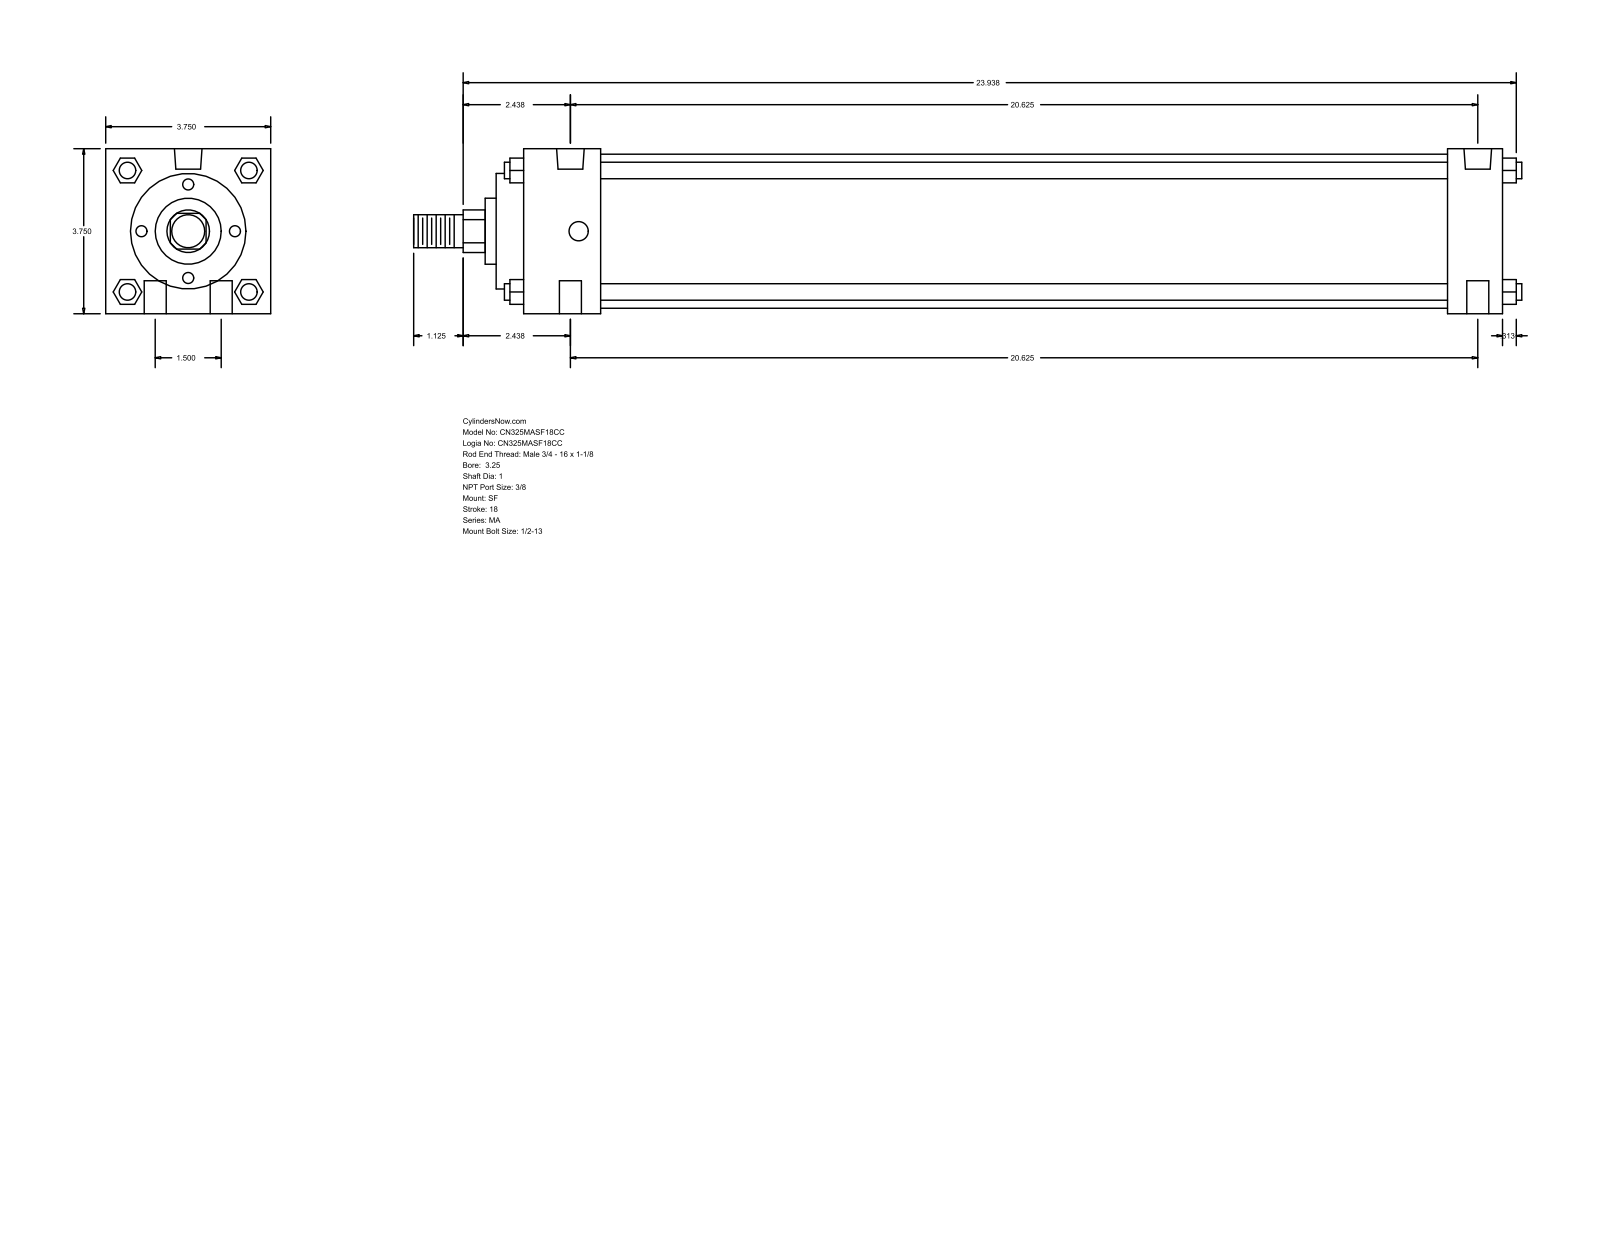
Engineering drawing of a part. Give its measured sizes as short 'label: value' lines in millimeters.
name: MA_SF__0325_1
written by: GSSL Pune (CONFIG_CONTROL_DESIGN)
unit: mm
bodies: 0 solids, 126 faces (95 planar, 31 cylindrical, 0 other)
size: 639.76 × 95.25 × 95.25
holes: 4× ⌀12.7, 2× ⌀11.11, 2× ⌀15.93
bosses: 4× ⌀9.53, 1× ⌀88.9, 1× ⌀66.67, 1× ⌀38.1, 1× ⌀25.4, 1× ⌀19.05
rounds: 1× R12.29
face distances: 95.24, 565.16, 533.41, 31.75, 44.46, 488.95, 520.7, 15.87, 60.33, 549.28
hole spacings: 19.05, 524.23, 523.88, 38.1, 525.26, 514.35
